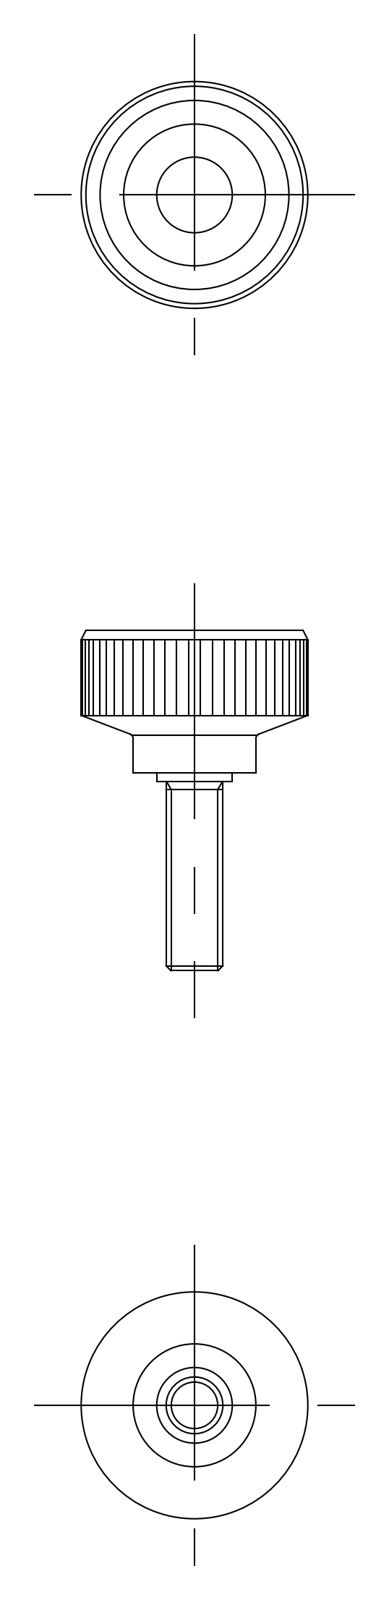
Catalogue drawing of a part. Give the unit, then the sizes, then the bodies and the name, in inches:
Units: inches
Overall size (bounding box): 1.417 × 0.945 × 0.945
Volume: 0.258 in³ · Surface area: 4.461 in²
Bodies: 2 solids, 35 faces (0 planar, 0 cylindrical, 35 other)
Part name (STEP PRODUCT): screw; knob; KKM_24_M6_20_5207_36
STEP written by: CADfix (AUTOMOTIVE_DESIGN)
